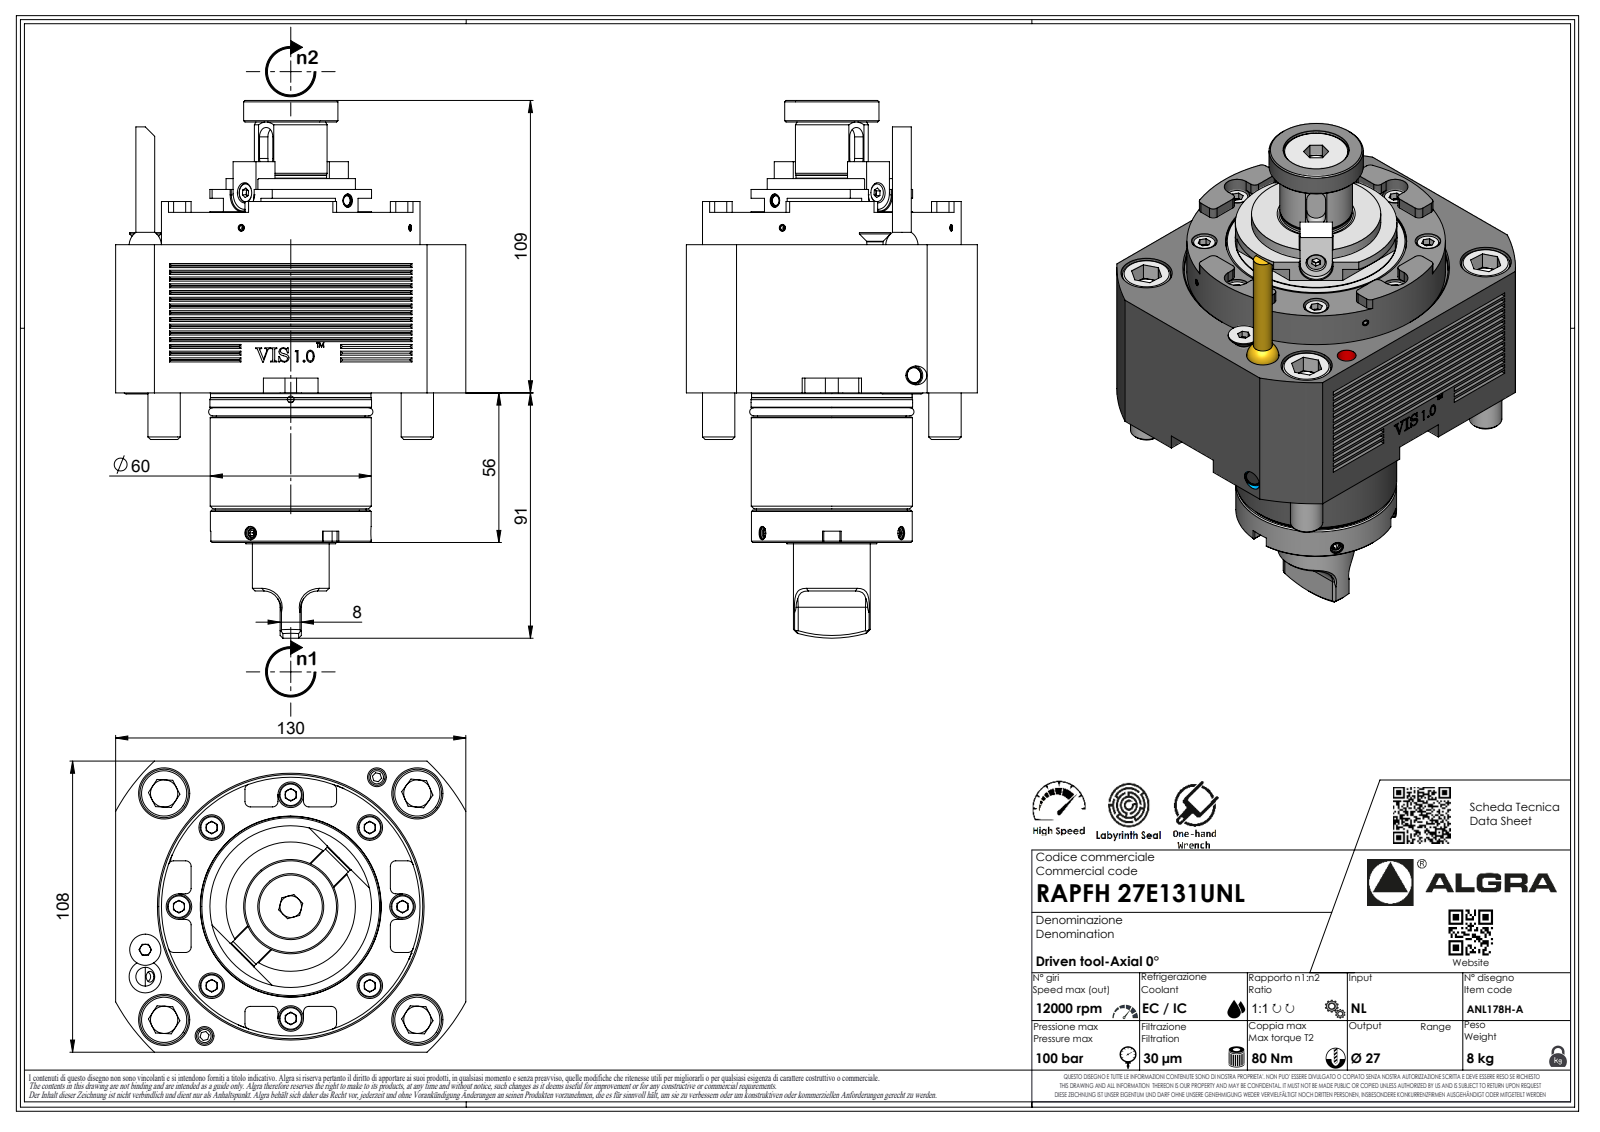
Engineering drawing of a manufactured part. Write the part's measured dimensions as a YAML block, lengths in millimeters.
part_name: "RAPFH27E131UNL"
step_written_by: "SolidWorks 2023 (AUTOMOTIVE_DESIGN)"
units: millimeters
bodies: {solids: 1, faces: 507, planar: 338, cylindrical: 93, other: 76}
overall_size: [199.5, 130, 108]
volume: 1059000
surface_area: 81494
round_holes:
  - {diameter: 2.1, count: 1}
  - {diameter: 4, count: 1}
round_bosses_or_shafts:
  - {diameter: 12, count: 4}
  - {diameter: 96, count: 1}
  - {diameter: 60, count: 1}
  - {diameter: 48, count: 1}
  - {diameter: 35, count: 1}
  - {diameter: 28.5, count: 1}
  - {diameter: 27, count: 1}
  - {diameter: 7, count: 1}
partial_cylinders:
  - {radius: 2, count: 25}
  - {radius: 6, count: 10}
  - {radius: 8, count: 8}
  - {radius: 0.33, count: 7}
  - {radius: 0.52, count: 7}
  - {radius: 3.7, count: 7}
  - {radius: 4.75, count: 4}
  - {radius: 0.21, count: 1}
face_to_face_distances: [55, 108, 12, 130, 67, 55.5, 110.5, 122.5, 61.5, 4]
